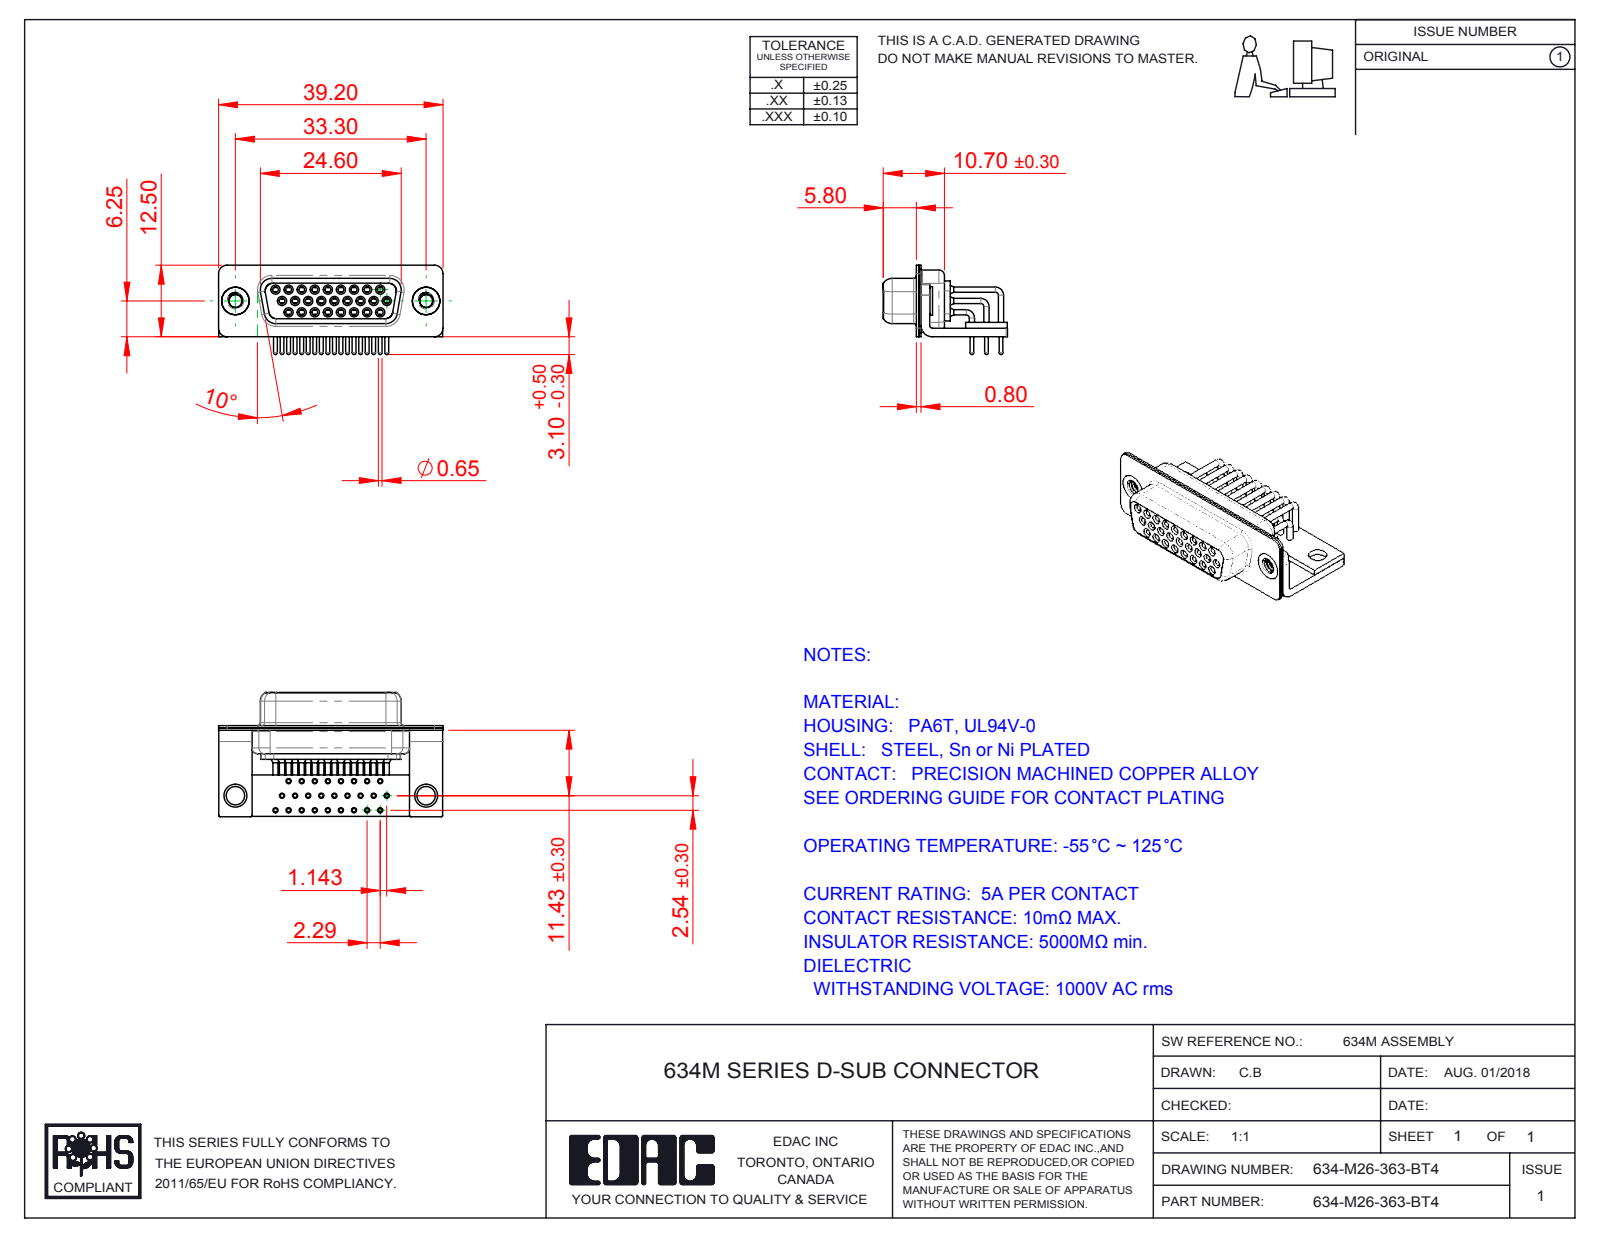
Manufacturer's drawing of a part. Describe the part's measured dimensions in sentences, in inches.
The part is named "634M 4-40 Threaded Rivet_Stabilizer; 634M Housing_26 Contacts; 634M Stabilizer Board_26 Contacts; 634-M26-363-BT4 (+6 more)". Its 3-D file was written by "SolidWorks 2016 (CONFIG_CONTROL_DESIGN)". It is 34 solids with 1759 faces: 483 planar, 809 cylindrical and 467 other. Overall it measures 1.543 by 0.854 by 0.614 inches. Its volume is 0.187 cubic inches and its surface area 15.14 square inches. Round holes: 26 of diameter 0.035, 26 of diameter 0.039, 26 of diameter 0.043, 26 of diameter 0.067, 26 of diameter 0.071, 26 of diameter 0.079, 2 of diameter 0.089, 2 of diameter 0.126, 2 of diameter 0.157, 2 of diameter 0.189. Round bosses or shafts: 27 of diameter 0.035, 26 of diameter 0.063, 26 of diameter 0.059, 26 of diameter 0.026, 2 of diameter 0.197, 2 of diameter 0.193, 1 of diameter 0.079. Partial cylindrical surfaces (rounded edges, fillets, slot ends): 16 of radius 0.01, 16 of radius 0.059, 13 of radius 0.079, 8 of radius 0.053, 8 of radius 0.063, 5 of radius 0.02, 4 of radius 0.024, 4 of radius 0.026. The main face-to-face distances are 0.016, 0.091, 0.031, 0.039, 0.059, 0.075, 0.368, 0.057, 0.352, 0.033. The hole center spacings are 0.18, 0.09, 0.09, 0.156, 0.238, 0.27, 0.168, 0.109.
